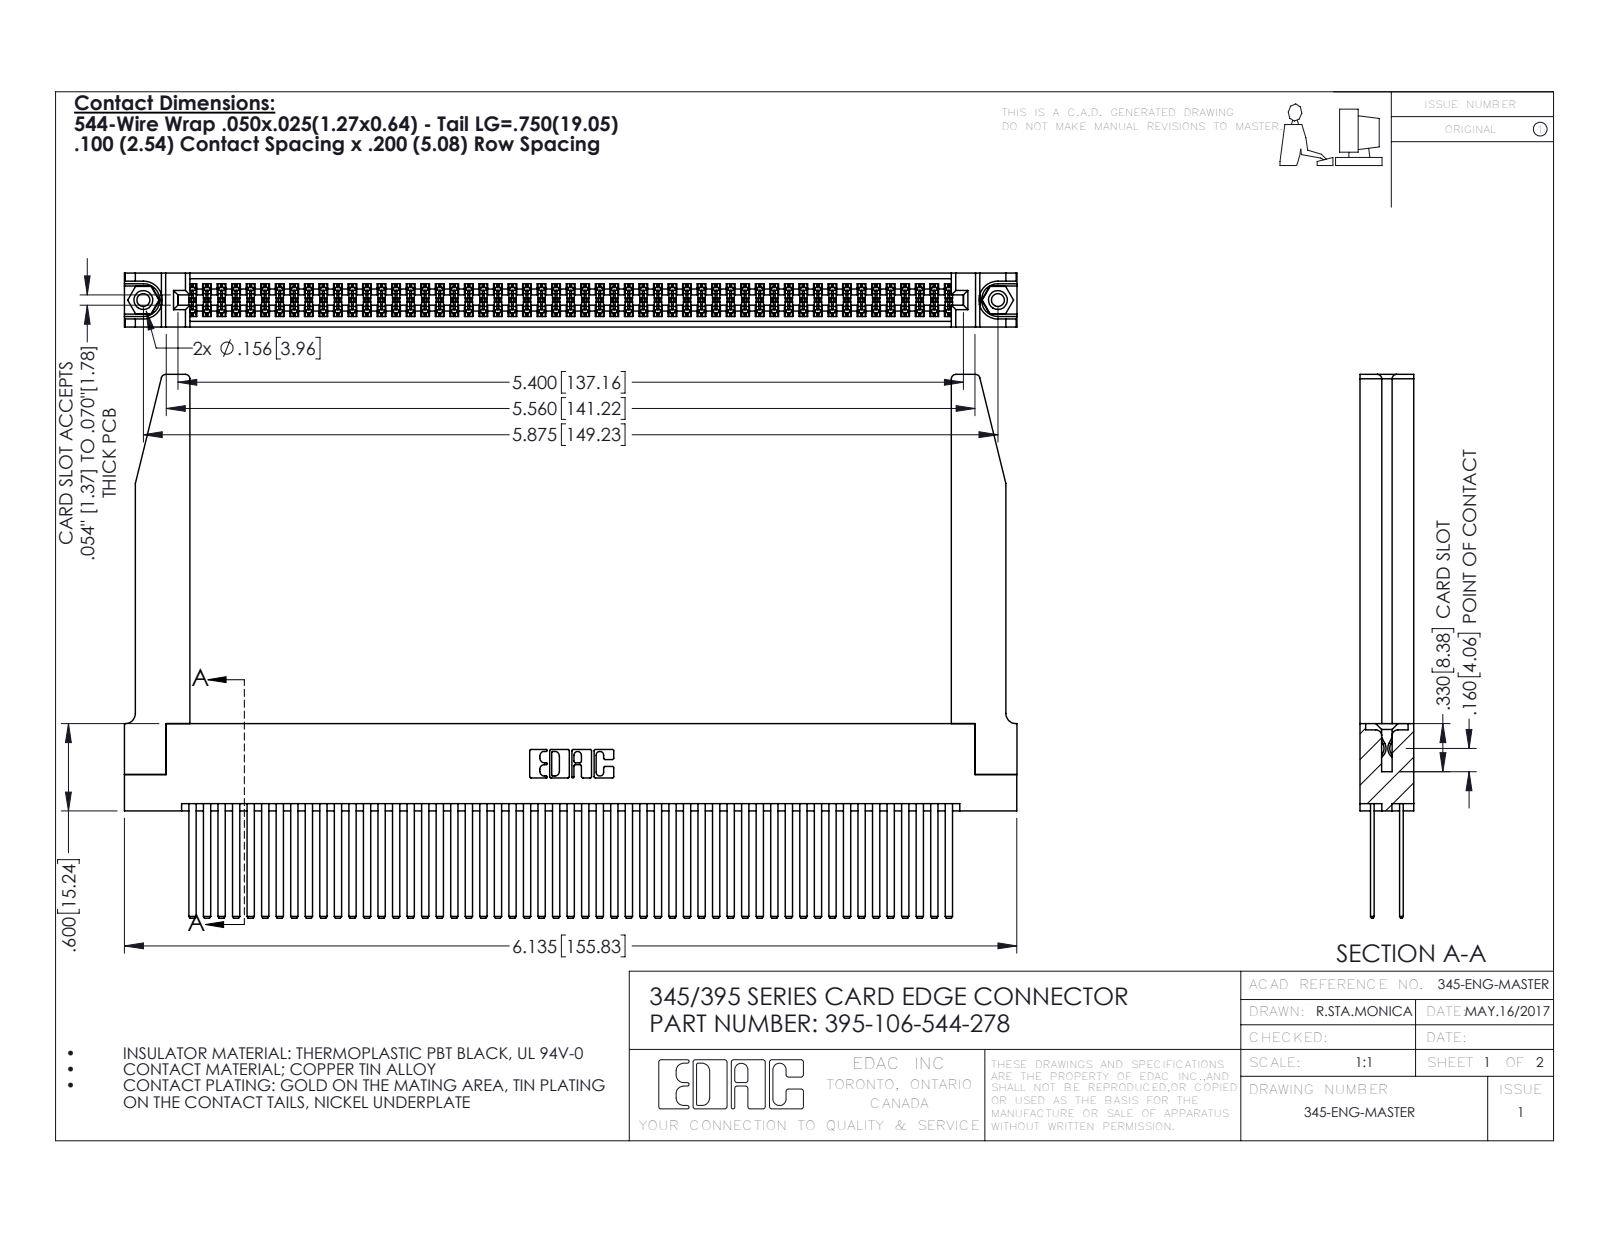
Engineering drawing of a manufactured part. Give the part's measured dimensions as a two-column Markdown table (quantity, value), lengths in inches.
| quantity | value |
| --- | --- |
| part name | 395-106-544-278; 345-292-001_345-293-144; 345 Part_Flush Mounting Lugs - 0.156 Dia-TH; 345-250-001_345-250-001-102 (+1 more) |
| STEP written by | SolidWorks 2016 (CONFIG_CONTROL_DESIGN) |
| units | inches |
| bodies | 111 solids, 5024 faces (3296 planar, 1676 cylindrical, 52 other) |
| overall size | 6.136 × 3.737 × 0.37 |
| volume | 1.495 in³ |
| surface area | 56.01 in² |
| round holes (diameter × count) | 0.089 × 2, 0.125 × 2, 0.156 × 2, 0.064 × 1 |
| round bosses / shafts (diameter × count) | 0.155 × 2 |
| partial cylindrical surfaces (radius × count) | 0.006 × 159, 0.01 × 22, 0.03 × 8, 0.007 × 6, 0.031 × 6, 0.026 × 3, 0.014 × 2, 0.019 × 2 |
| main face-to-face distances | 0.072, 0.298, 0.2, 0.098, 0.272, 0.025, 0.37, 0.225, 0.175, 0.148 |
| hole center spacings | 0.27, 5.639, 5.875 |
